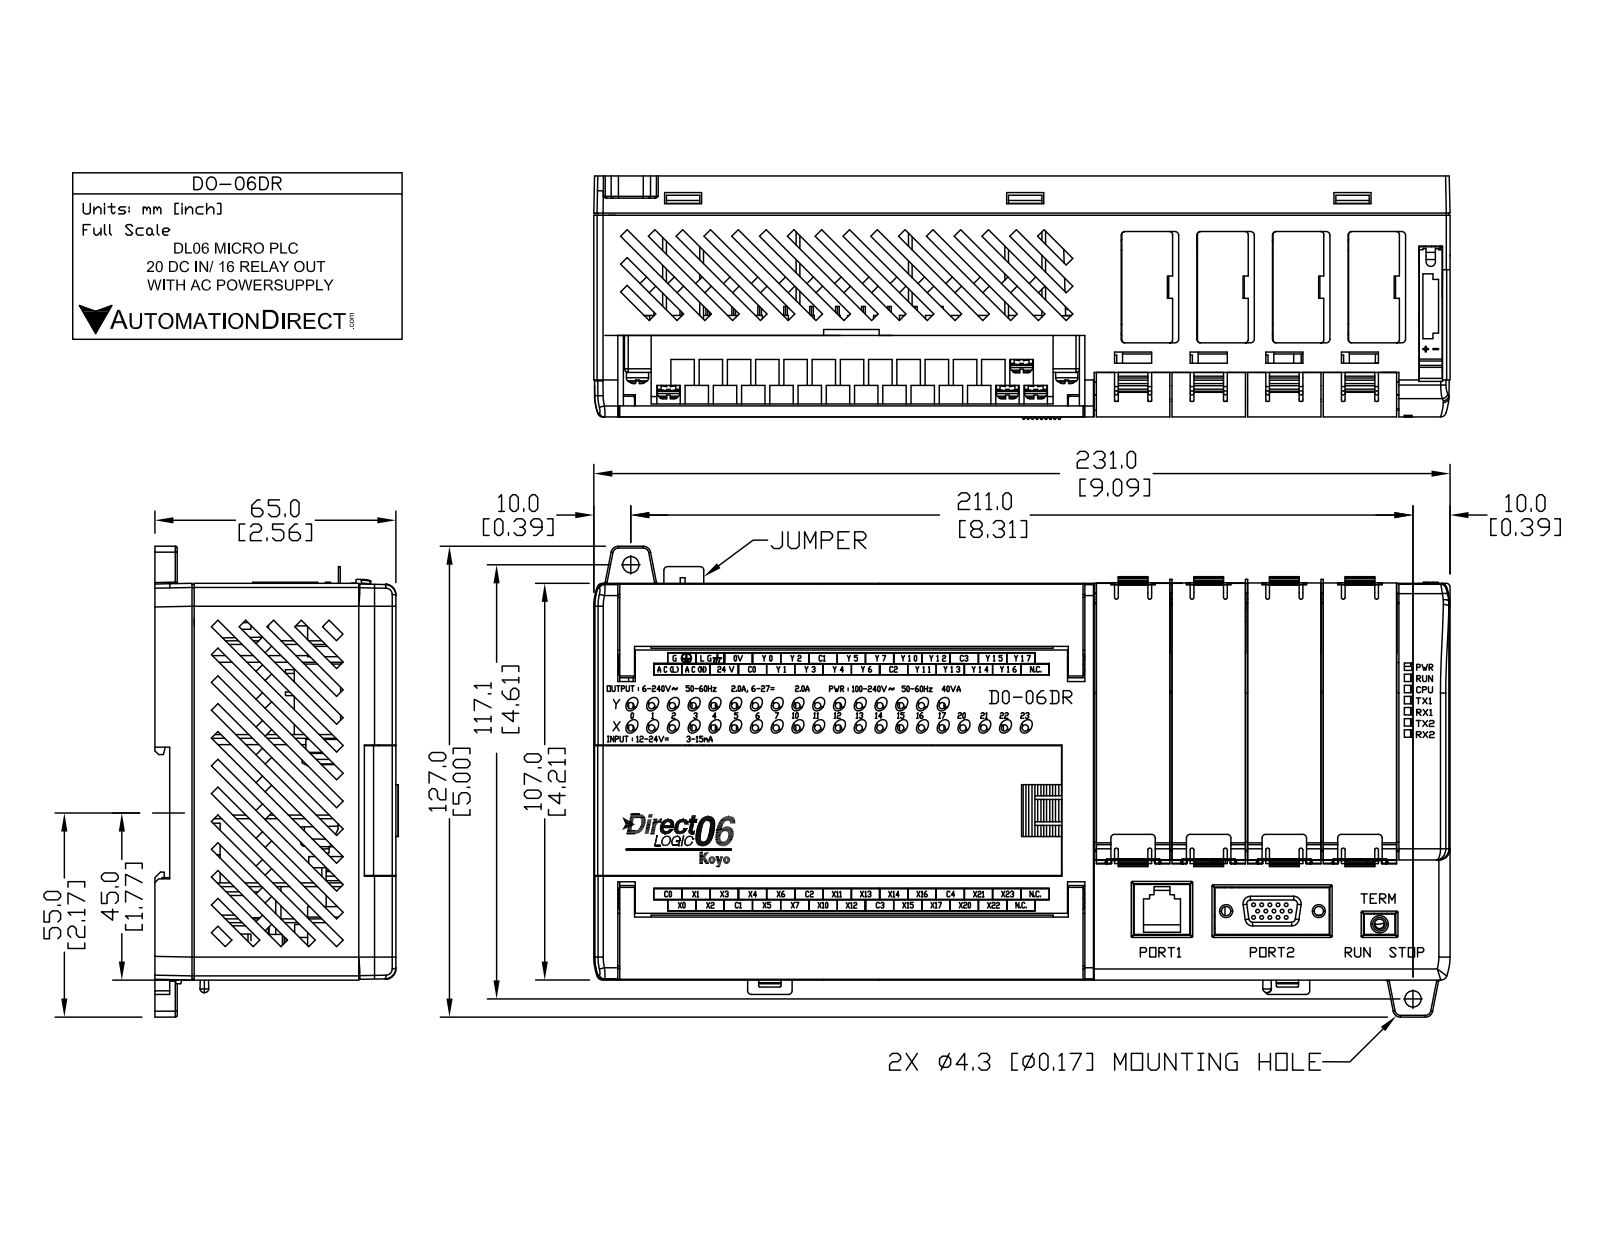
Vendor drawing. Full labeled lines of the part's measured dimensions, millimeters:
Part name (STEP PRODUCT): D0-06DR
STEP written by: SolidWorks 2009 (AUTOMOTIVE_DESIGN)
Units: millimetres
Bodies: 1 solid, 1426 faces (925 planar, 189 cylindrical, 312 other)
Overall size (bounding box): 230.9 × 127.1 × 65.2
Volume: 262 200 mm³ · Surface area: 199 400 mm²
Round holes (diameter × count): ⌀3 ×4, ⌀2 ×2, ⌀4.3 ×2
Round bosses / shafts (diameter × count): ⌀4.7 ×54, ⌀6.4 ×4, ⌀4.4 ×1, ⌀3.6 ×1
Partial cylindrical surfaces — rounded edges, fillets, slot ends (radius × count): R1.3 ×8, R1.7 ×5, R1.6 ×4, R2 ×4, R1 ×2, R1.6 ×2, R1.9 ×1, R62.8 ×1
Main face-to-face distances: 2.2, 2.2, 62.8, 4, 58.8, 65, 228.7, 60.6, 6.2, 56.6
Hole centre spacings: 82.8, 117.1, 143.5, 17.2, 23.8, 35.5, 42.7, 56
